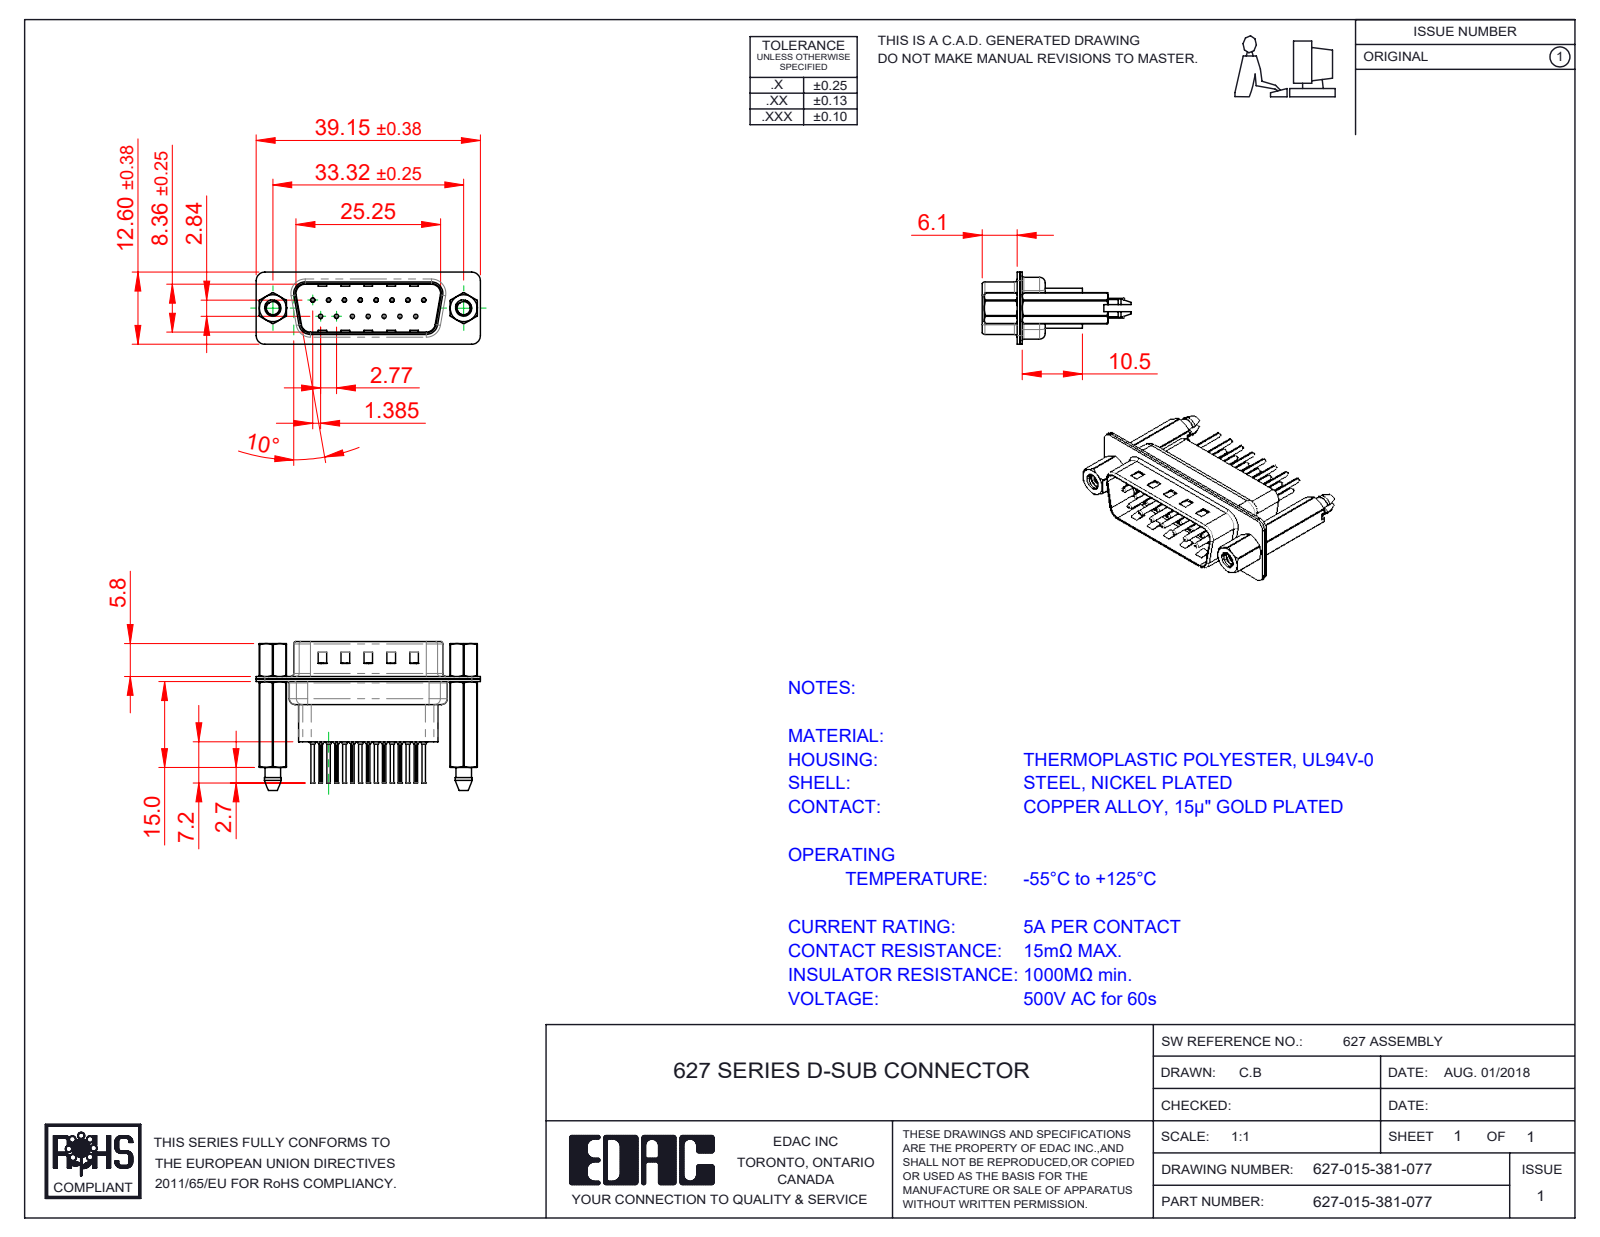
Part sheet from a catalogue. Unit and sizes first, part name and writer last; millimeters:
Units: millimetres
Overall size (bounding box): 39.15 × 25.9 × 12.6
Round holes (diameter × count): ⌀0.2 ×15, ⌀0.35 ×15, ⌀1.1 ×15, ⌀1.6 ×15, ⌀2.26 ×2, ⌀2.29 ×2, ⌀4 ×2, ⌀4.8 ×2
Round bosses / shafts (diameter × count): ⌀2 ×15, ⌀1.5 ×15, ⌀0.75 ×15, ⌀0.6 ×15, ⌀4.9 ×2, ⌀2.79 ×2
Partial cylindrical surfaces — rounded edges, fillets, slot ends (radius × count): R0.1 ×30, R1.5 ×18, R2 ×12, R1.6 ×10, R0.5 ×8, R0.25 ×4, R0.6 ×4, R0.65 ×4
Main face-to-face distances: 0.4, 0.45, 4.76, 0.9, 0.82, 9.58, 1.5, 16.66, 0.68, 7.68
Hole centre spacings: 3.16, 2.77, 5.54, 8.31, 11.08, 5.03, 5.04, 7.48
Volume: 3 148 mm³ · Surface area: 8 038 mm²
Bodies: 22 solids, 2044 faces (553 planar, 826 cylindrical, 665 other)
Part name (STEP PRODUCT): 627 Contact Row 2_61; 627 4-40 Hex Standoff; 627 Housing_15 HP; 627 Contact Row 1_61 (+4 more)
STEP written by: SolidWorks 2020 (CONFIG_CONTROL_DESIGN)
